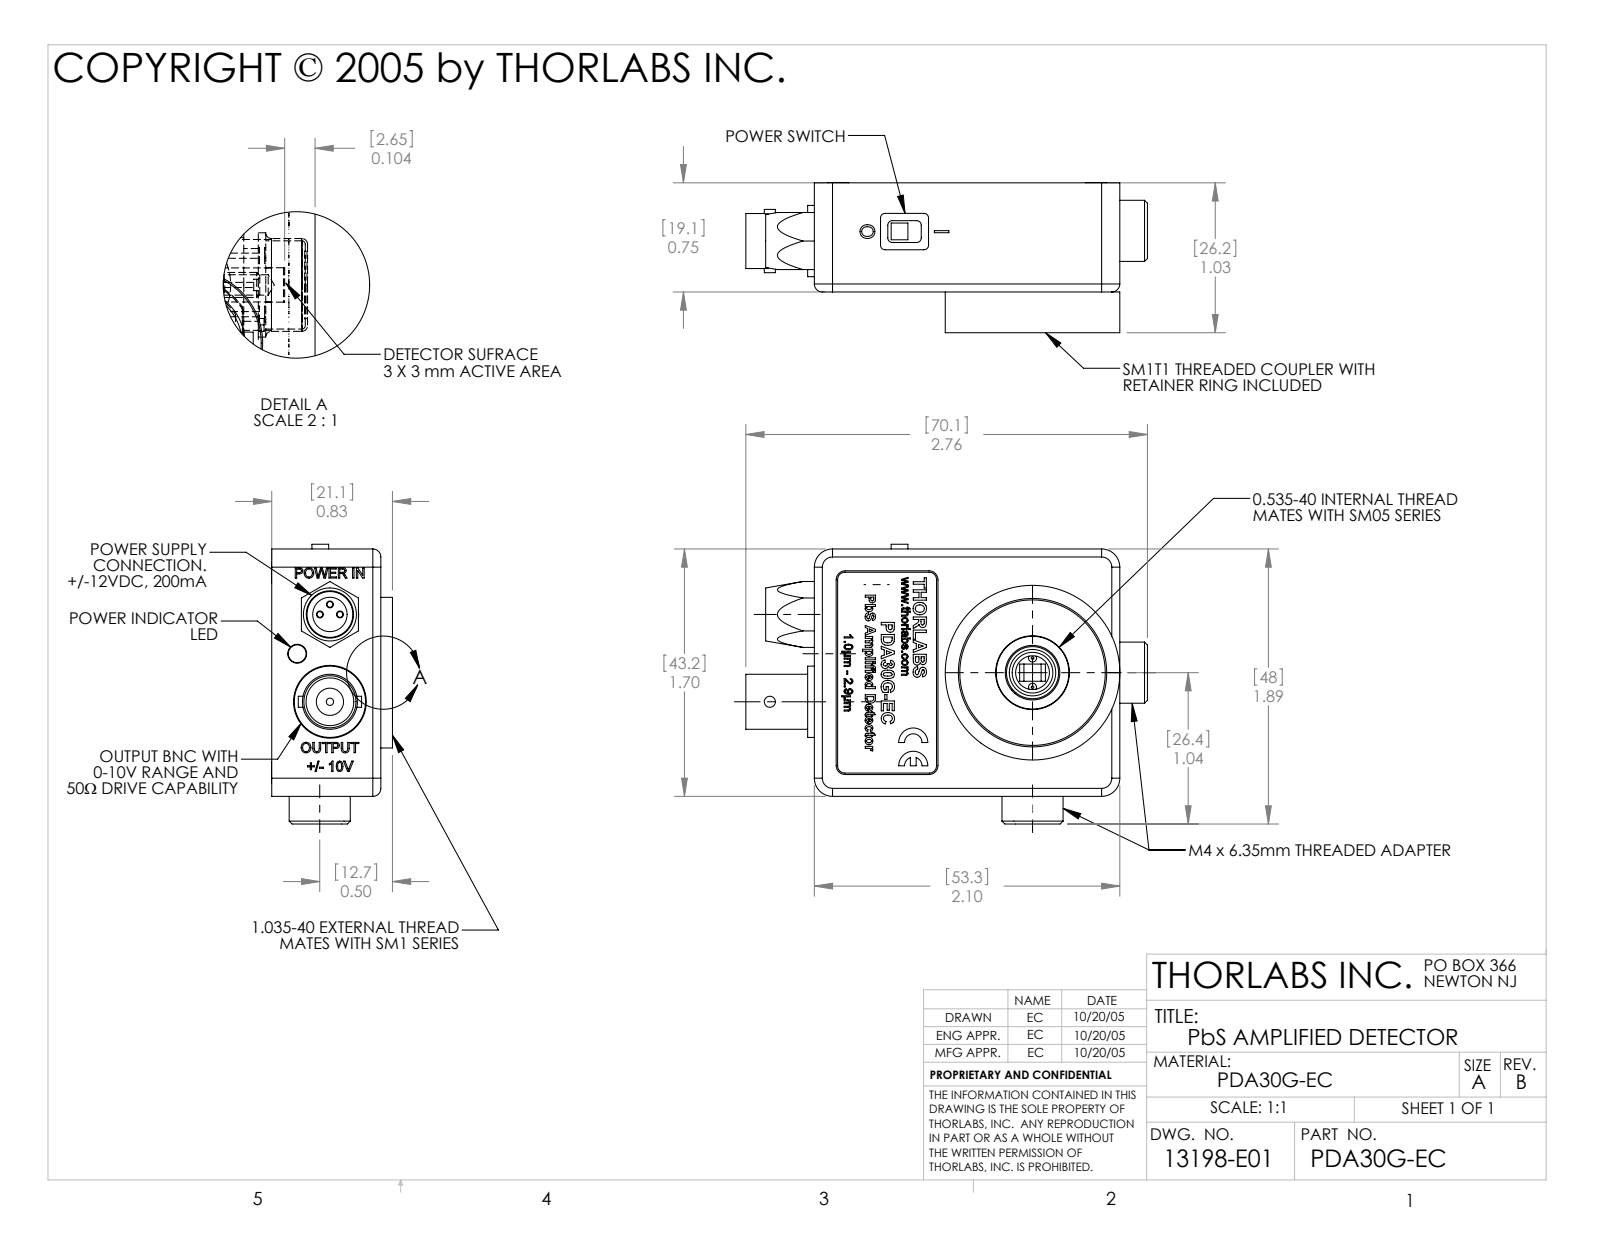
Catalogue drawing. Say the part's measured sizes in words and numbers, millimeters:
The part is named "13198-E0W". Its 3-D file was written by "SolidWorks 2009 (AUTOMOTIVE_DESIGN)". It is 17 solids with 1781 faces: 957 planar, 271 cylindrical and 553 other. Overall it measures 70.13 by 48.83 by 26.2 millimeters. Its volume is 23 765 cubic millimeters and its surface area 26 848 square millimeters. Round holes: 7 of diameter 1.78, 7 of diameter 2.44, 4 of diameter 3.17, 4 of diameter 5.08, 3 of diameter 0.71, 3 of diameter 1, 2 of diameter 1.4, 2 of diameter 3.3, 2 of diameter 3.81, 2 of diameter 5, 1 of diameter 1.27, 1 of diameter 1.32. Round bosses or shafts: 4 of diameter 3.73, 4 of diameter 2.18, 3 of diameter 0.45, 2 of diameter 10.67, 2 of diameter 5.99, 1 of diameter 30.48, 1 of diameter 26.29, 1 of diameter 12.7. Partial cylindrical surfaces (rounded edges, fillets, slot ends): 22 of radius 3.17, 12 of radius 0.79, 8 of radius 2.41, 4 of radius 1.27, 4 of radius 1.4, 4 of radius 1.59, 3 of radius 0.25, 2 of radius 1.52. The main face-to-face distances are 1.59, 2.54, 13.08, 11.49, 1.27, 11.48, 9.89, 1.6, 1.78, 4.19. The hole center spacings are 3.6, 22.16, 1.75, 2.54, 37.1, 2.47, 2.55, 3.59.
